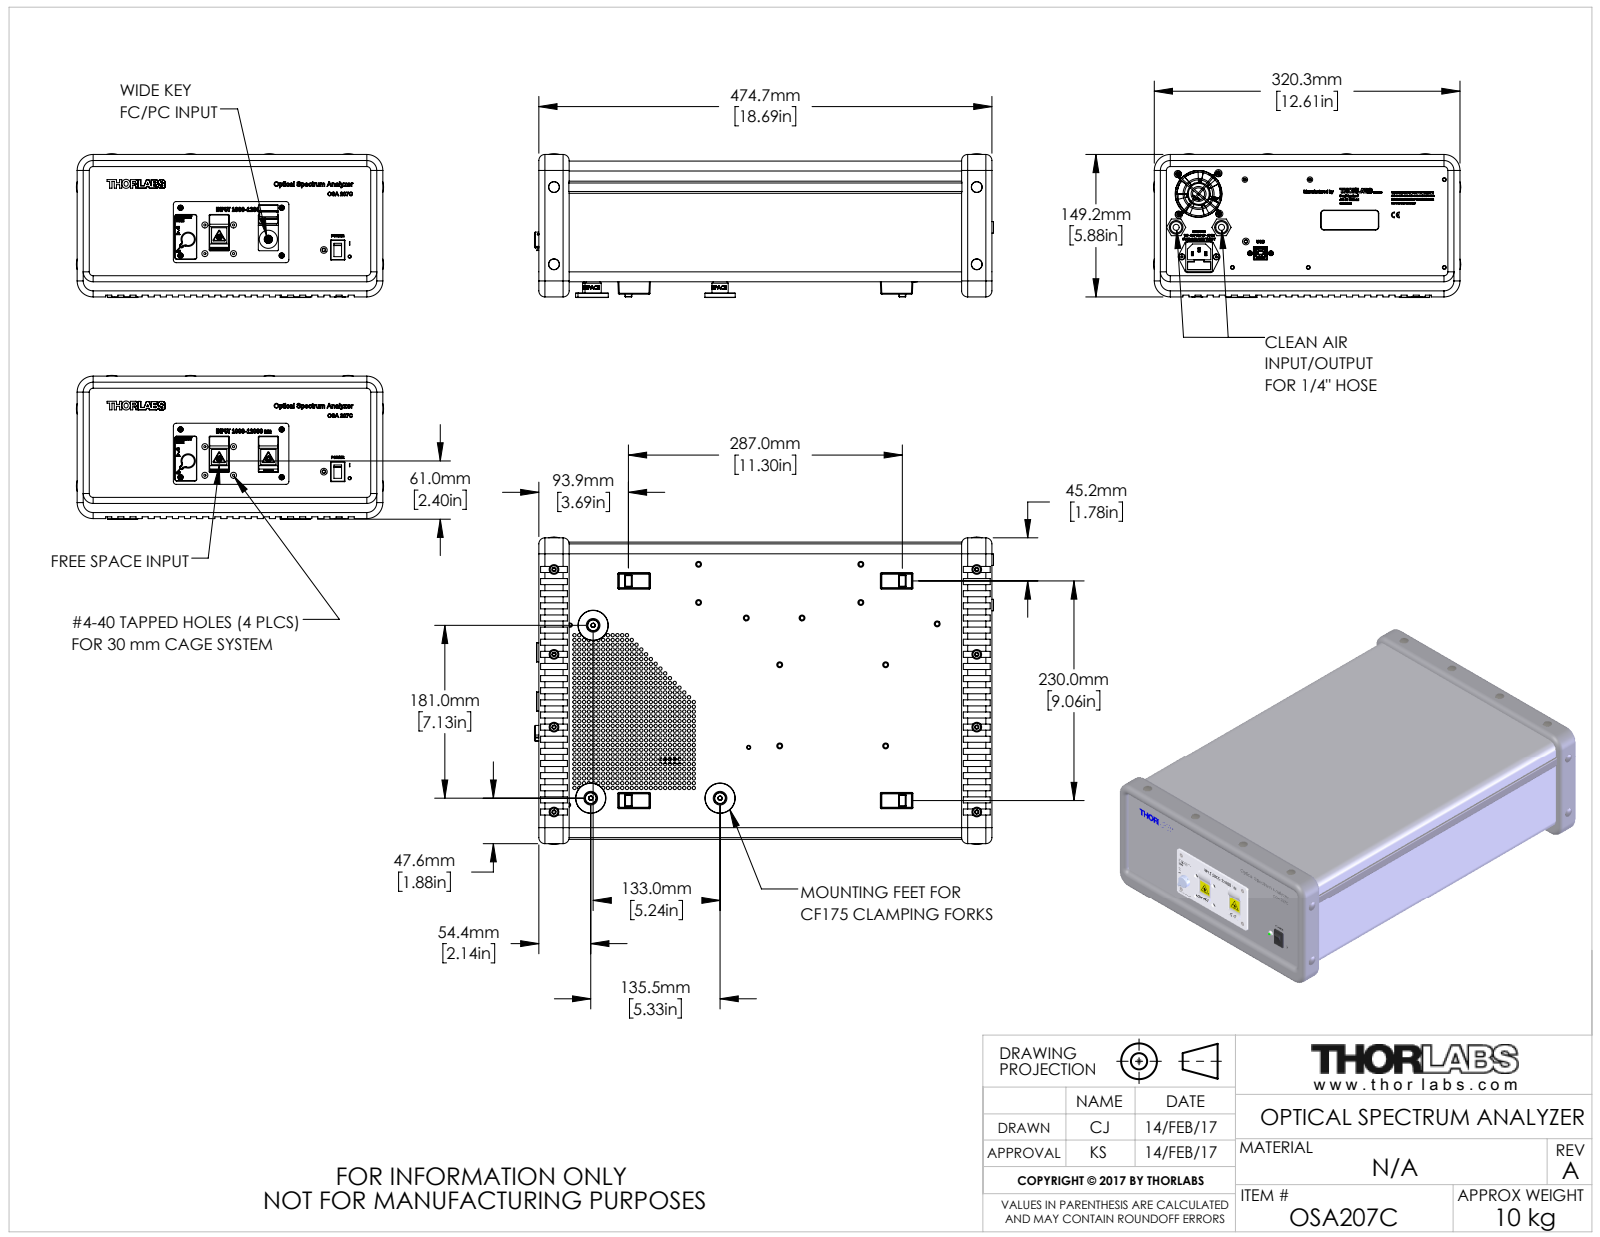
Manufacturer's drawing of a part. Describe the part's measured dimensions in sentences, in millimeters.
The part is named "FKK 201 0305 MF6S M3x5; OMS 110 0100_STN; FKK 209 0031; WU-A-3 (+8 more)". Its 3-D file was written by "SolidWorks 2016 (AUTOMOTIVE_DESIGN)". It is 254 solids with 17358 faces: 8819 planar, 3970 cylindrical and 4569 other. Overall it measures 480.91 by 321.82 by 150.61 millimeters. Its volume is 1 900 000 cubic millimeters and its surface area 1 632 000 square millimeters. Round holes: 753 of diameter 3.5, 49 of diameter 2.5, 28 of diameter 2.05, 26 of diameter 3.2, 17 of diameter 3.3, 15 of diameter 3, 13 of diameter 2.26, 12 of diameter 1.2, 12 of diameter 5.08, 12 of diameter 11.43, 11 of diameter 5, 9 of diameter 3.1. Round bosses or shafts: 36 of diameter 3, 22 of diameter 4, 20 of diameter 5, 17 of diameter 6, 15 of diameter 7, 13 of diameter 2.4, 12 of diameter 11.05, 12 of diameter 5.38. Partial cylindrical surfaces (rounded edges, fillets, slot ends): 91 of radius 0.5, 56 of radius 1, 48 of radius 0.27, 48 of radius 0.91, 47 of radius 1.5, 40 of radius 3, 24 of radius 0.16, 24 of radius 0.55. The main face-to-face distances are 1, 125.4, 126.4, 124.4, 306.6, 461, 90.65, 34.75, 307.6, 305.6. The hole center spacings are 16, 25.5, 32, 105, 275.05, 5, 10, 230.
